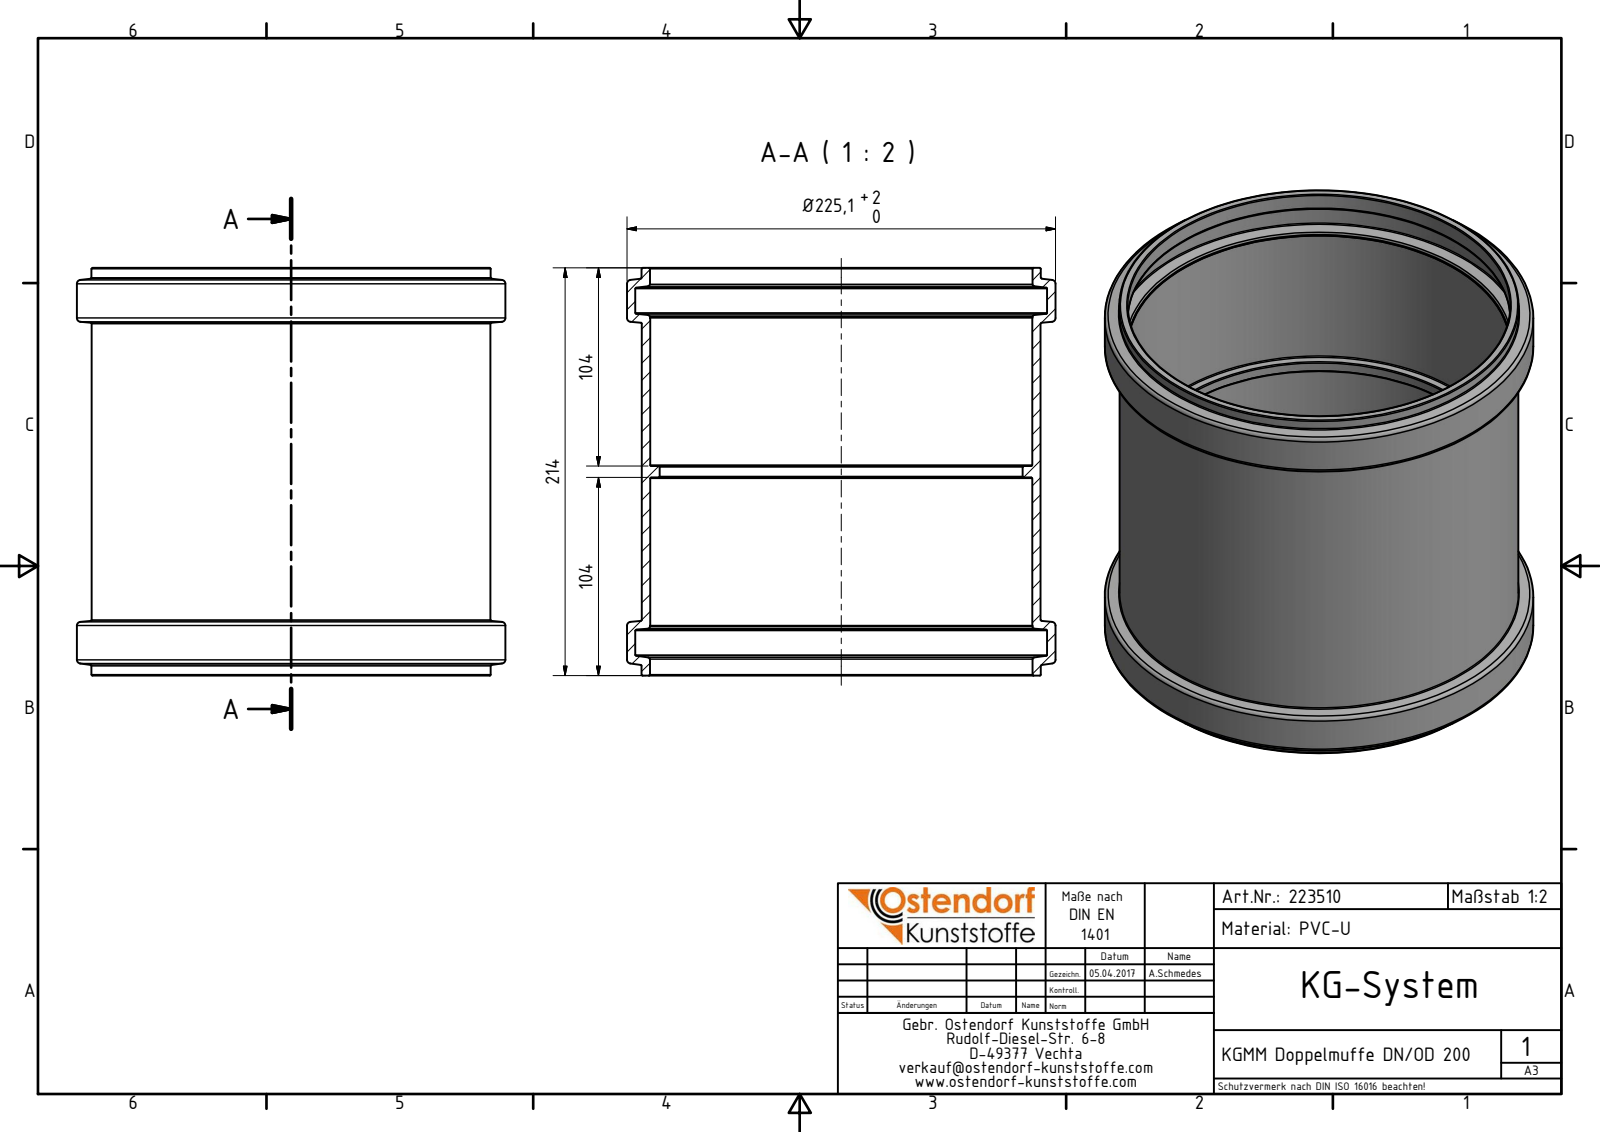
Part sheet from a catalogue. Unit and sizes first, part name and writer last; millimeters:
Units: millimetres
Overall size (bounding box): 225.1 × 225.1 × 214
Round holes (diameter × count): ⌀190.6 ×1, ⌀200.6 ×1, ⌀200.9 ×1, ⌀216.3 ×1
Round bosses / shafts (diameter × count): ⌀225.1 ×1, ⌀209.7 ×1, ⌀209.4 ×1
Main face-to-face distances: 104, 110, 6, 214, 26.17, 187.83, 77.83, 83.83, 161.66
Volume: 712 864 mm³ · Surface area: 323 708 mm²
Bodies: 1 solid, 52 faces (6 planar, 14 cylindrical, 32 other)
Part name (STEP PRODUCT): 223510 KGMM Doppelmuffe DN_OD 200
STEP written by: Autodesk Inventor 2016 (AUTOMOTIVE_DESIGN)
